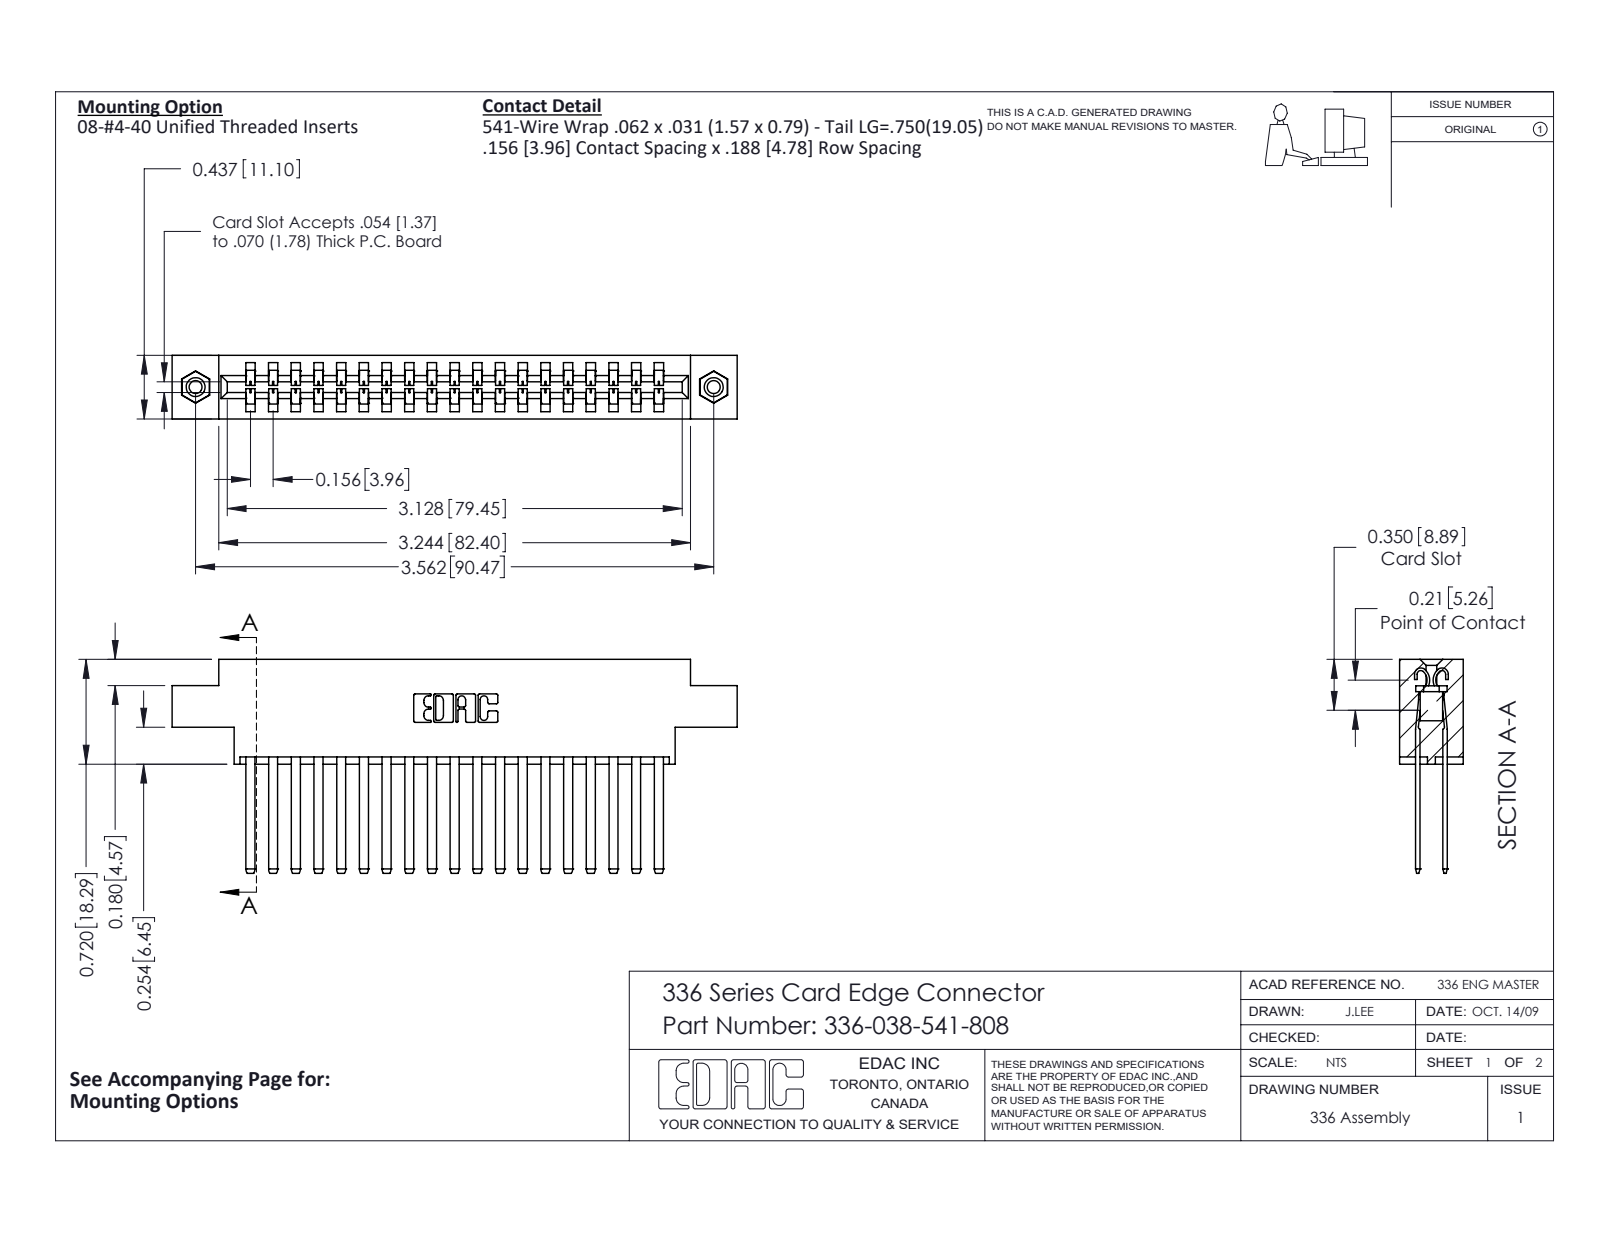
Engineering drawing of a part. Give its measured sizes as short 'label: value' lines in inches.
name: 336-038-541-808; 336-290-001_336-290-541; 345-250-001_345-250-003-102; 336 Part_Offset - .156 Dia - TI
written by: SolidWorks 2020 (CONFIG_CONTROL_DESIGN)
unit: in
bodies: 41 solids, 1774 faces (1094 planar, 664 cylindrical, 16 other)
size: 3.885 × 1.47 × 0.437
volume: 0.883 in³; area: 28.11 in²
holes: 2× ⌀0.089, 2× ⌀0.125, 2× ⌀0.156
bosses: 2× ⌀0.155
rounds: 76× R0.004, 38× R0.056, 22× R0.01, 6× R0.007, 6× R0.031, 4× R0.022, 4× R0.04, 3× R0.026
face distances: 0.188, 0.328, 0.14, 0.297, 0.109, 0.031, 0.437, 0.033, 0.181, 0.146
hole spacings: 3.562
